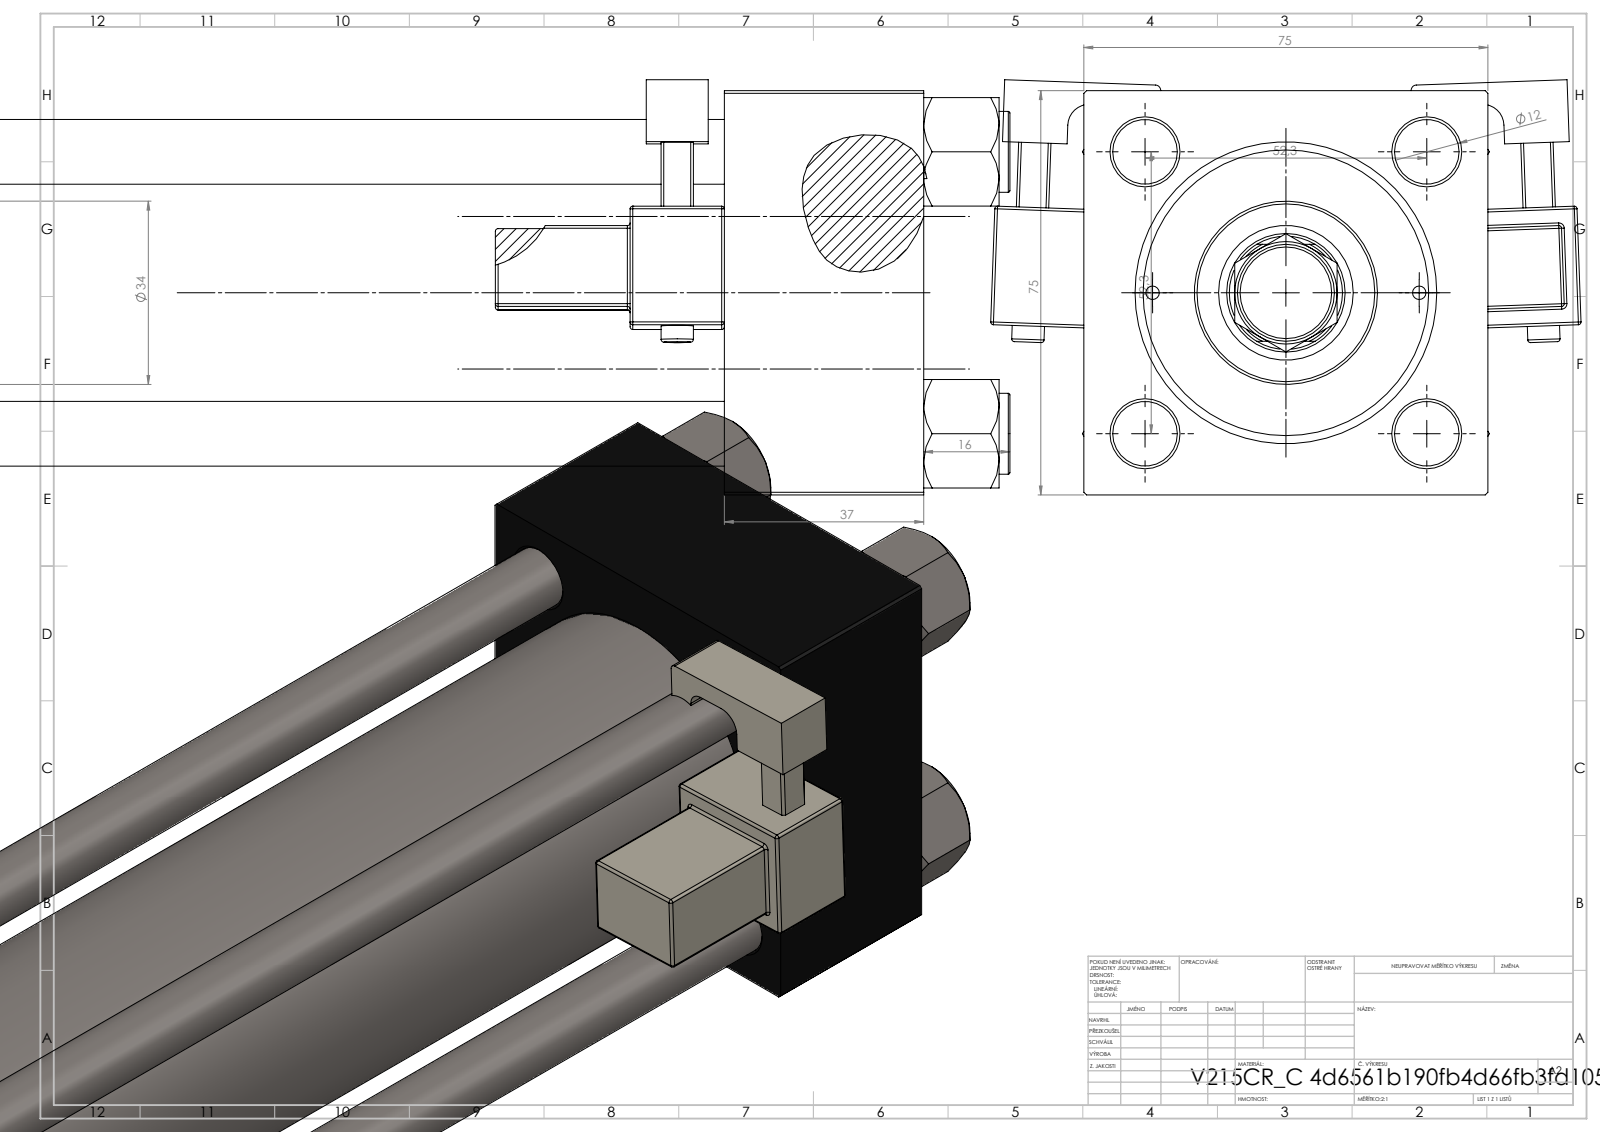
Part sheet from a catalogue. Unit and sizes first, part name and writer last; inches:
Units: inches
Overall size (bounding box): 18.031 × 4.314 × 3.033
Round holes (diameter × count): ⌀0.472 ×4, ⌀0.098 ×2, ⌀0.276 ×2, ⌀0.825 ×2, ⌀1.181 ×2, ⌀0.413 ×1, ⌀0.866 ×1, ⌀0.984 ×1, ⌀1.614 ×1, ⌀1.969 ×1, ⌀2.087 ×1
Round bosses / shafts (diameter × count): ⌀0.591 ×4, ⌀0.236 ×2, ⌀2.205 ×1, ⌀1.339 ×1, ⌀0.709 ×1, ⌀0.433 ×1
Partial cylindrical surfaces — rounded edges, fillets, slot ends (radius × count): R0.02 ×48, R0.039 ×2, R0.098 ×2, R0.157 ×2, R0.413 ×1
Main face-to-face distances: 2.953, 1.457, 15.118, 13.661, 12.795, 11.339, 2.323, 13.988, 12.531, 1.193
Hole centre spacings: 1.031, 1.456, 2.059, 2.253, 0.974, 2.912, 1.949, 12.736
Volume: 61.76 in³ · Surface area: 448.7 in²
Bodies: 14 solids, 1360 faces (602 planar, 154 cylindrical, 604 other)
Part name (STEP PRODUCT): V215CR_C_Body; V215CR_C_TYCINKA; V215CR_MSU; V215CR_VCP_C (+3 more)
STEP written by: SolidWorks 2019 (CONFIG_CONTROL_DESIGN)
